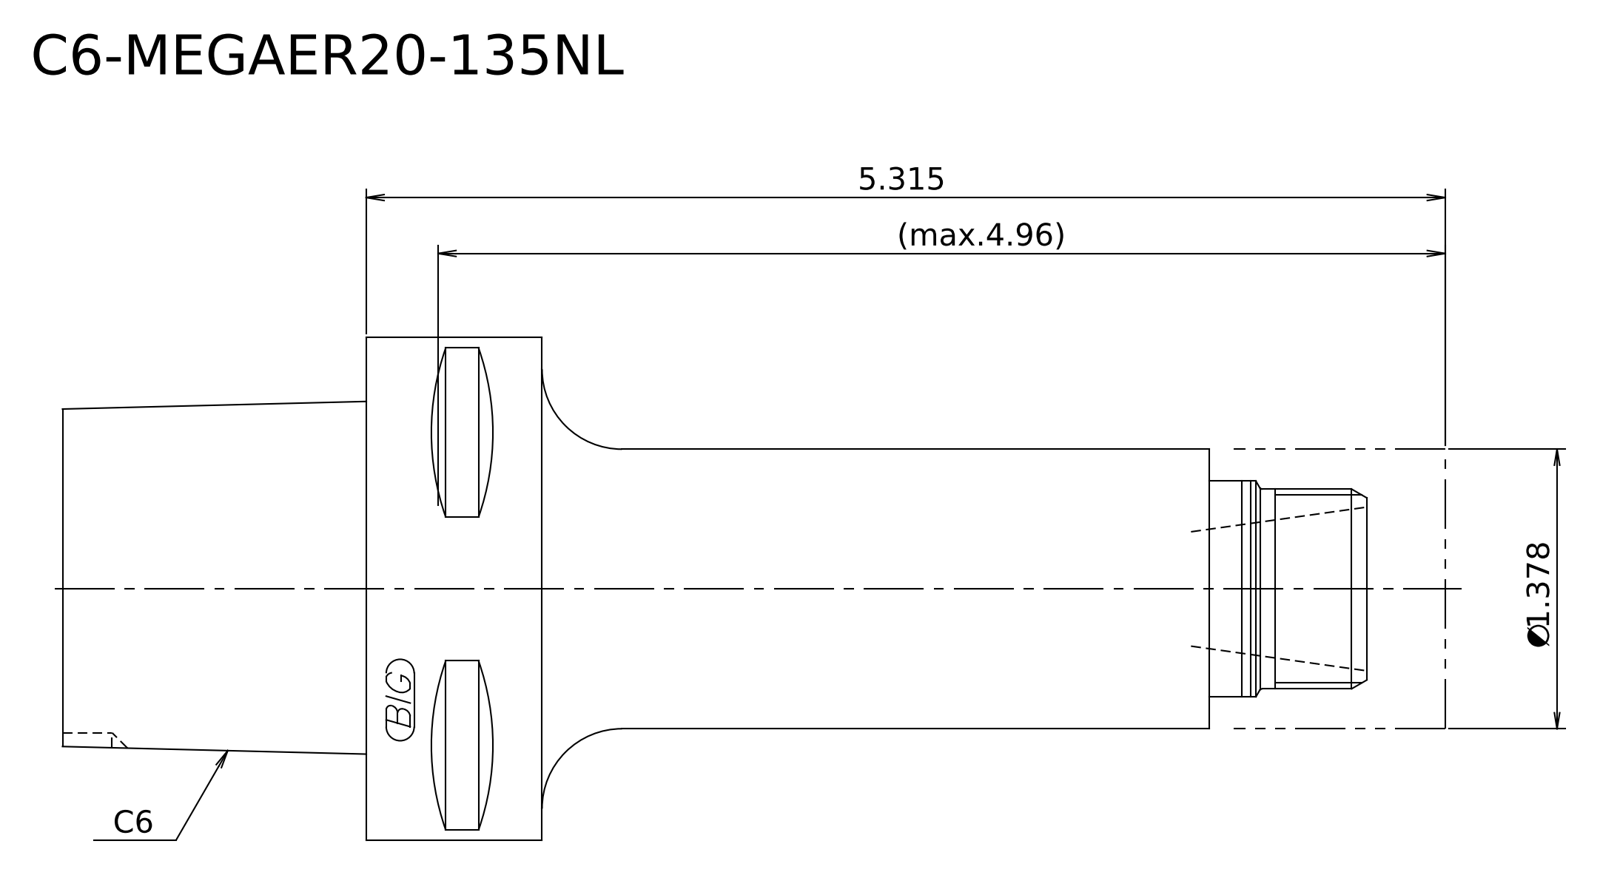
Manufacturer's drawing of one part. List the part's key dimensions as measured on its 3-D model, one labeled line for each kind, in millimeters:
STEP written by: Kubotek KeyCreator 2011 V10.0.2 (22737) (automotive_design)
Units: millimetres
Bodies: 2 solids, 18 faces (7 planar, 5 cylindrical, 6 other)
Overall size (bounding box): 173 × 63 × 63
Volume: 245 822 mm³ · Surface area: 30 607 mm²
Round bosses / shafts (diameter × count): ⌀63 ×1, ⌀35 ×1, ⌀27 ×1, ⌀25 ×1
Main face-to-face distances: 38, 108.5, 146.5, 26.5, 135, 173, 113, 86.5, 22, 60
